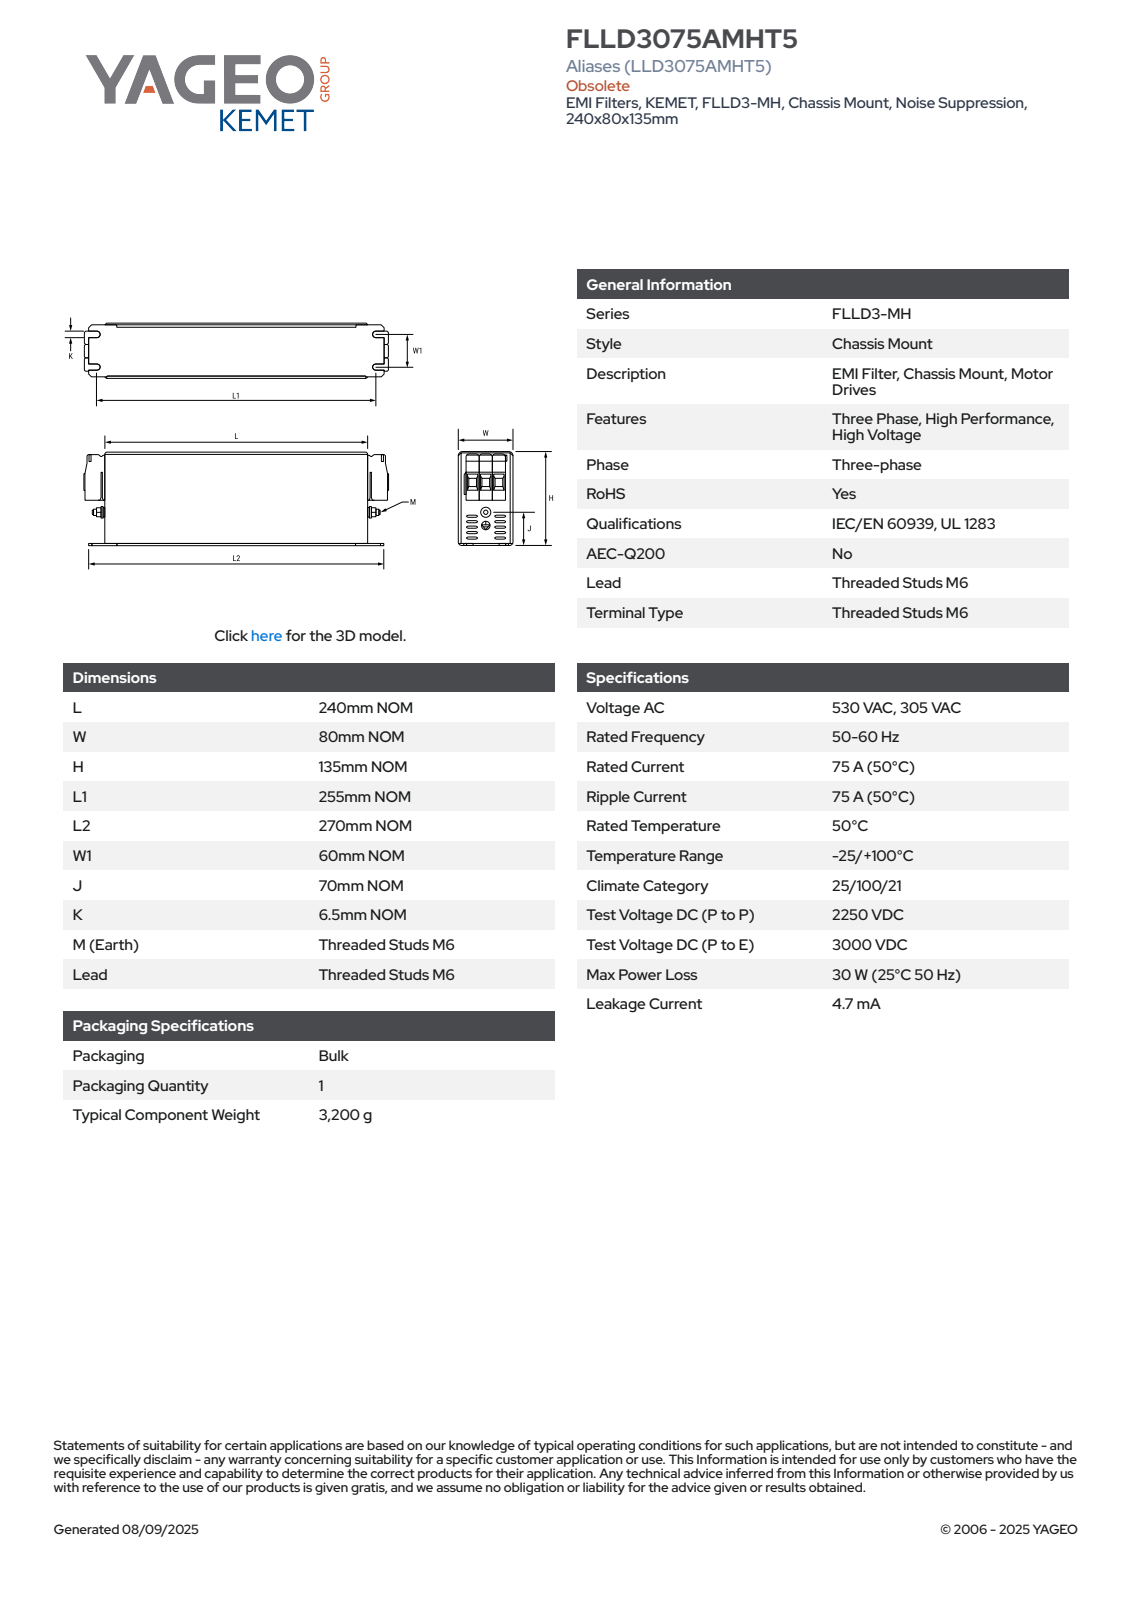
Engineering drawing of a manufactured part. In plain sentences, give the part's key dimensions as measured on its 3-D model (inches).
The part is named "EFC_KFLLD3MH_L240W80H135L1255L2270W160". Its 3-D file was written by "SolidWorks 2014 (AUTOMOTIVE_DESIGN)". It is 4 solids with 153 faces: 117 planar, 32 cylindrical and 4 other. Overall it measures 10.63 by 5.315 by 3.15 inches. Its volume is 159.9 cubic inches and its surface area 207.4 square inches. Round bosses or shafts: 1 of diameter 0.367, 1 of diameter 0.276, 1 of diameter 0.236. Partial cylindrical surfaces (rounded edges, fillets, slot ends): 8 of radius 0.157, 4 of radius 0.079, 4 of radius 0.128. The main face-to-face distances are 3.15, 5.315, 9.449, 9.764, 0.315, 0.039, 0.669, 5.276, 0.63, 10.079.
